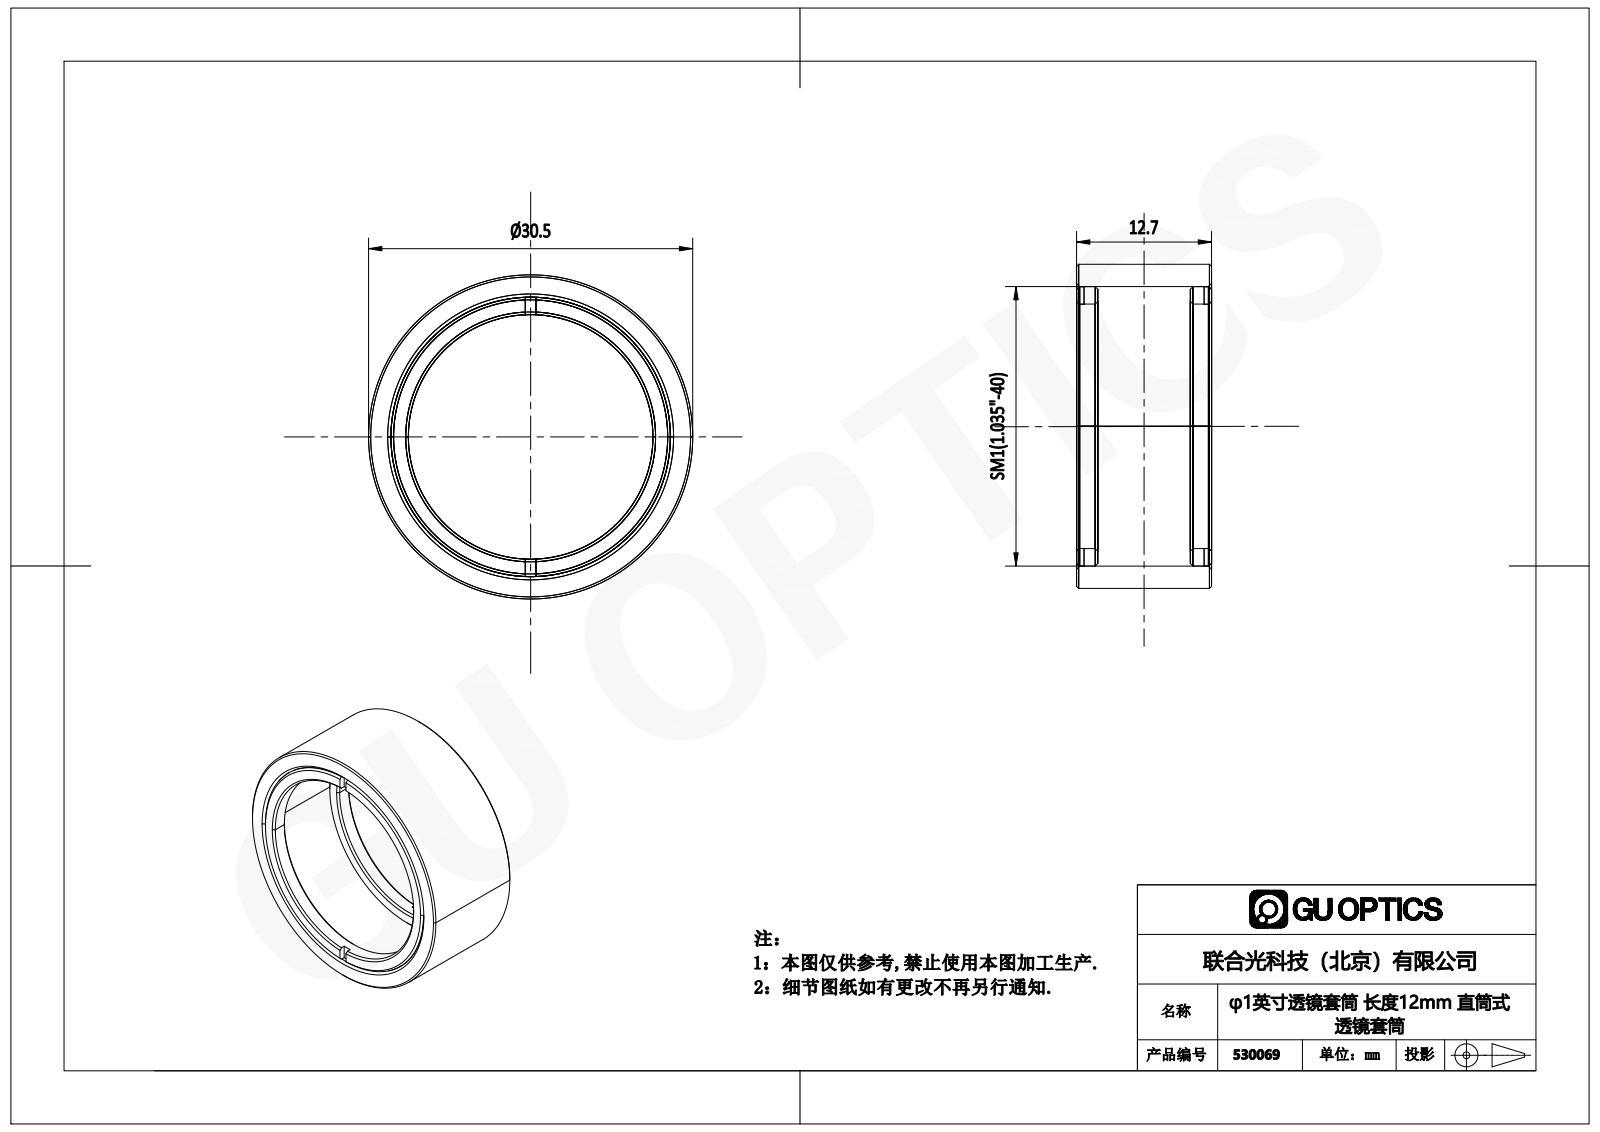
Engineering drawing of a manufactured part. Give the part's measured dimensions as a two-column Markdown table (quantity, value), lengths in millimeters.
| quantity | value |
| --- | --- |
| STEP written by | SolidWorks 2018 (AUTOMOTIVE_DESIGN) |
| units | millimeters |
| bodies | 0 solids, 60 faces (20 planar, 12 cylindrical, 28 other) |
| overall size | 30.5 × 30.5 × 12.7 |
| round holes (diameter × count) | 23.01 × 1, 26.3 × 1 |
| round bosses / shafts (diameter × count) | 30.5 × 1, 26.29 × 1 |
| main face-to-face distances | 12.7, 2, 10.7, 8.7, 0.7, 12, 1.3, 10, 1, 11.3 |
